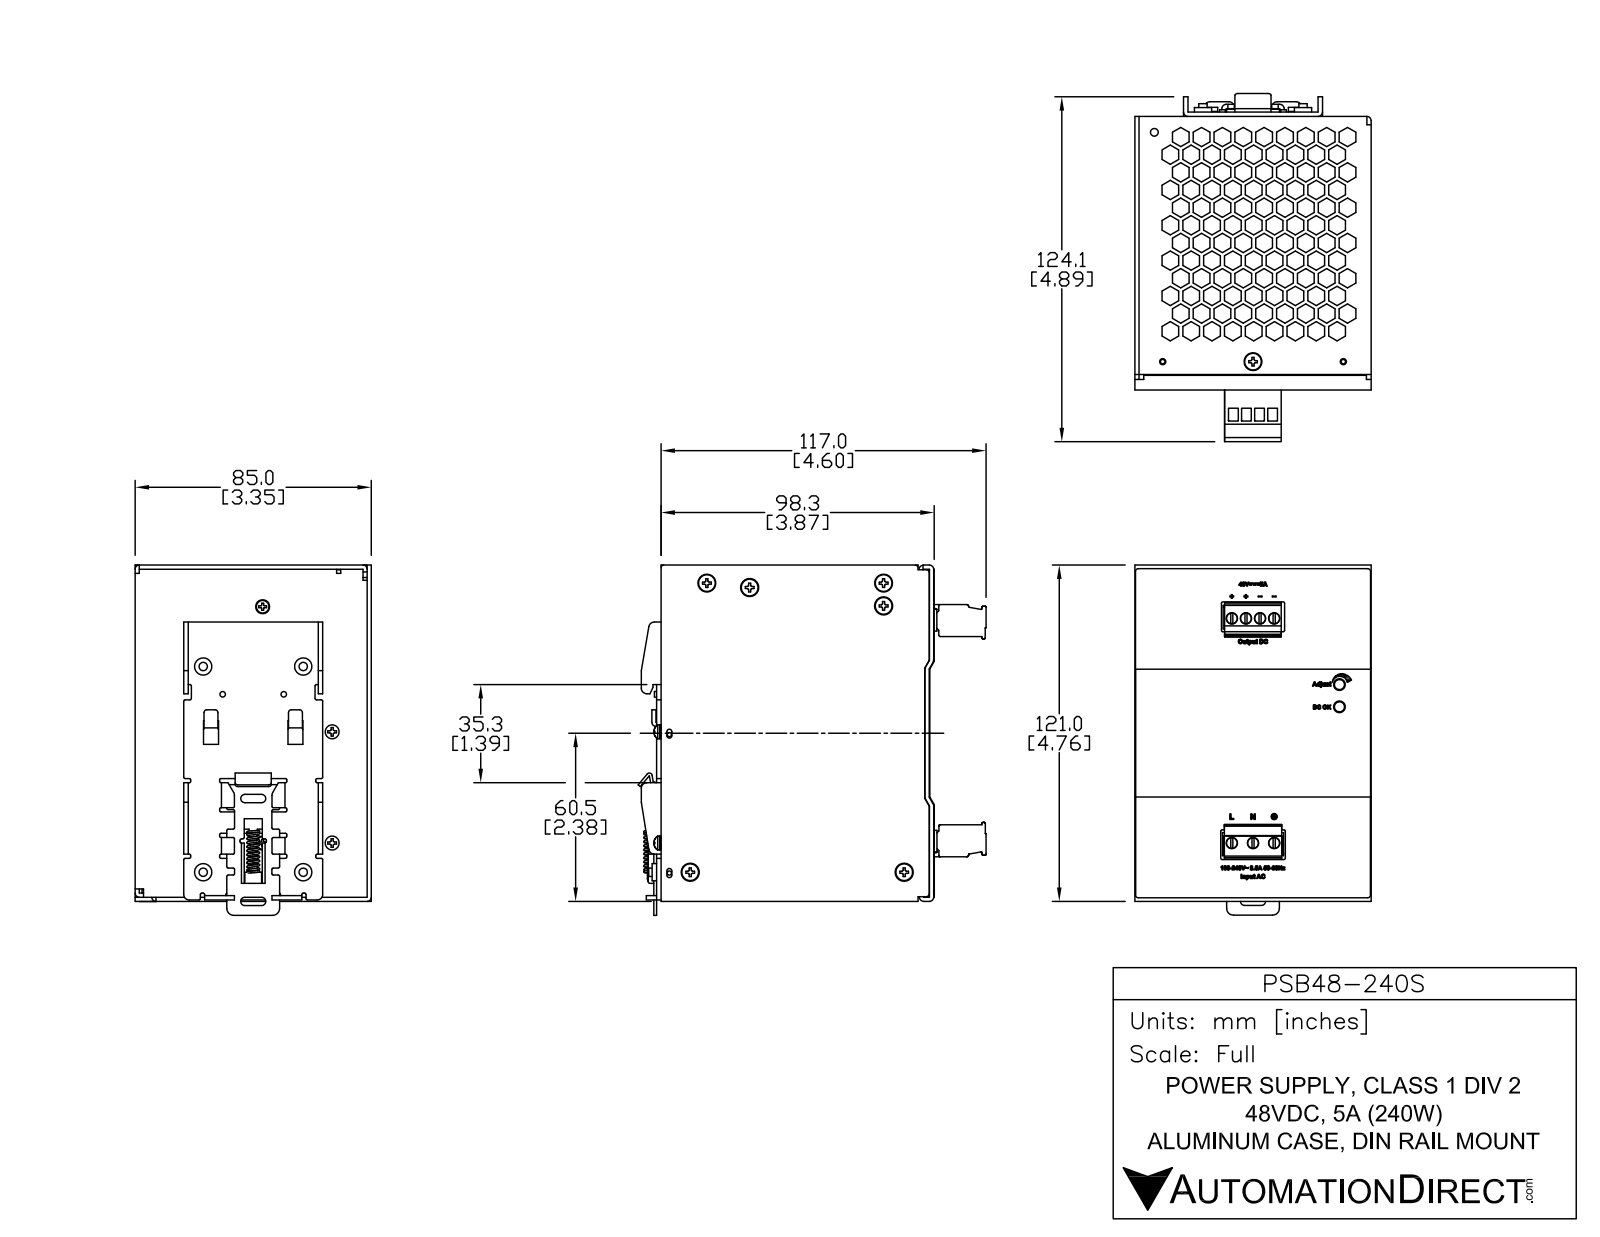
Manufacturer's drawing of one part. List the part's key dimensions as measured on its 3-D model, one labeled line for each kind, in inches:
Part name (STEP PRODUCT): 2968118703_DCT-1187; 3462026200_2; 310330060000; 324467780000 (+8 more)
STEP written by: SolidWorks 2014 (AUTOMOTIVE_DESIGN)
Units: inches
Bodies: 59 solids, 5168 faces (3473 planar, 954 cylindrical, 741 other)
Overall size (bounding box): 4.961 × 4.93 × 3.35
Volume: 10.06 in³ · Surface area: 444.1 in²
Round holes (diameter × count): ⌀0.157 ×14, ⌀0.098 ×11, ⌀0.159 ×7, ⌀0.134 ×6, ⌀0.165 ×5, ⌀0.256 ×4, ⌀0.118 ×3, ⌀0.063 ×2, ⌀0.079 ×2, ⌀0.087 ×2, ⌀0.094 ×2, ⌀0.11 ×1
Round bosses / shafts (diameter × count): ⌀0.236 ×13, ⌀0.118 ×11, ⌀0.156 ×7, ⌀0.098 ×7, ⌀0.161 ×5, ⌀0.157 ×5, ⌀0.205 ×4, ⌀0.106 ×4
Partial cylindrical surfaces — rounded edges, fillets, slot ends (radius × count): R0.02 ×154, R0.039 ×51, R0.03 ×37, R0.035 ×27, R0.016 ×20, R0.059 ×19, R0.004 ×18, R0.006 ×14
Main face-to-face distances: 0.059, 0.063, 0.017, 3.287, 3.13, 0.28, 3.067, 0.22, 3.008, 0.157
Hole centre spacings: 0.2, 0.3, 0.394, 0.4, 0.481, 0.6, 1.096, 1.208
